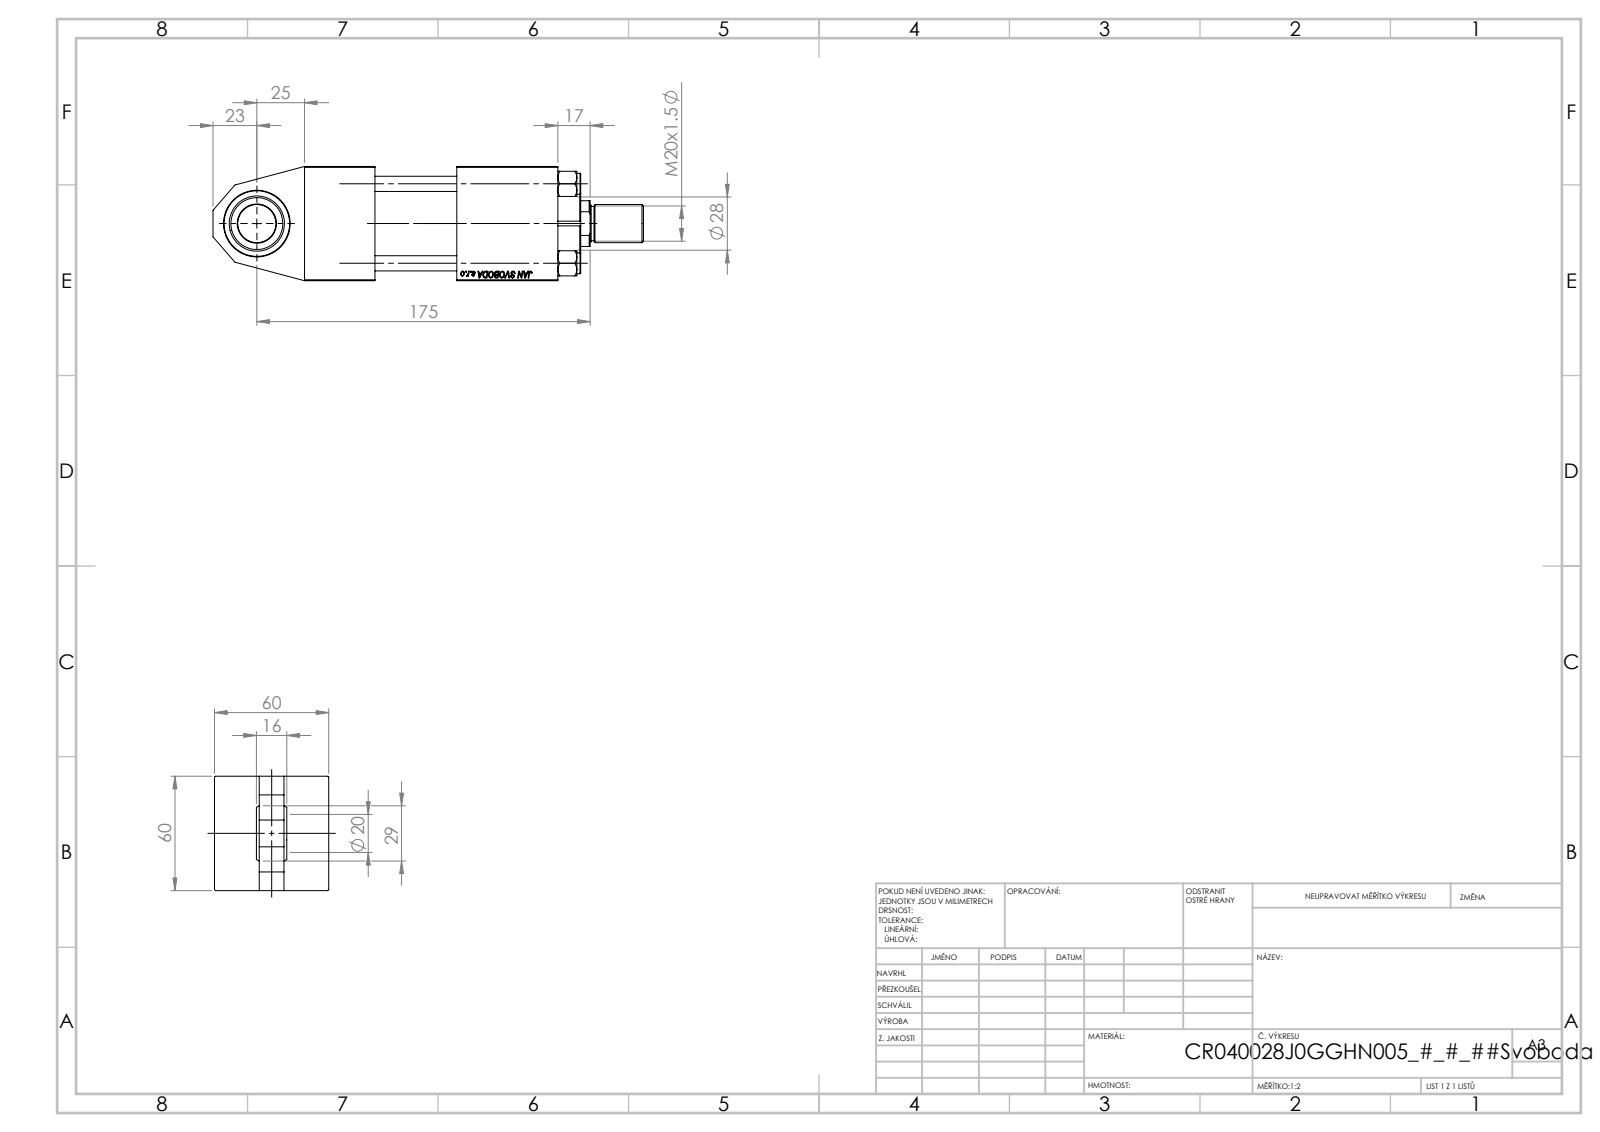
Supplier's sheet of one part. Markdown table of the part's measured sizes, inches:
| quantity | value |
| --- | --- |
| part name | NUT_M5_J; V215_VC_A; ROD_END_AH; V215CR_J_VNITRNI_KROUZEK (+3 more) |
| STEP written by | SolidWorks 2019 (CONFIG_CONTROL_DESIGN) |
| units | inches |
| bodies | 13 solids, 1161 faces (523 planar, 92 cylindrical, 546 other) |
| overall size | 8.898 × 2.362 × 2.362 |
| volume | 26.21 in³ |
| surface area | 178.5 in² |
| round holes (diameter × count) | 0.315 × 4, 0.098 × 2, 0.276 × 2, 0.656 × 2, 0.945 × 2, 0.728 × 1, 0.787 × 1, 1.102 × 1, 1.22 × 1, 1.378 × 1, 1.575 × 1, 1.772 × 1 |
| round bosses / shafts (diameter × count) | 0.433 × 4, 1.811 × 1, 1.654 × 1, 0.787 × 1, 0.709 × 1 |
| partial cylindrical surfaces (radius × count) | 0.531 × 1 |
| main face-to-face distances | 2.362, 1.437, 0.925, 1.457, 3.15, 1.693, 2.087, 5.236, 3.78, 0.512 |
| hole center spacings | 0.821, 1.161, 1.642, 1.832, 0.817, 2.322, 1.634, 3.051 |
